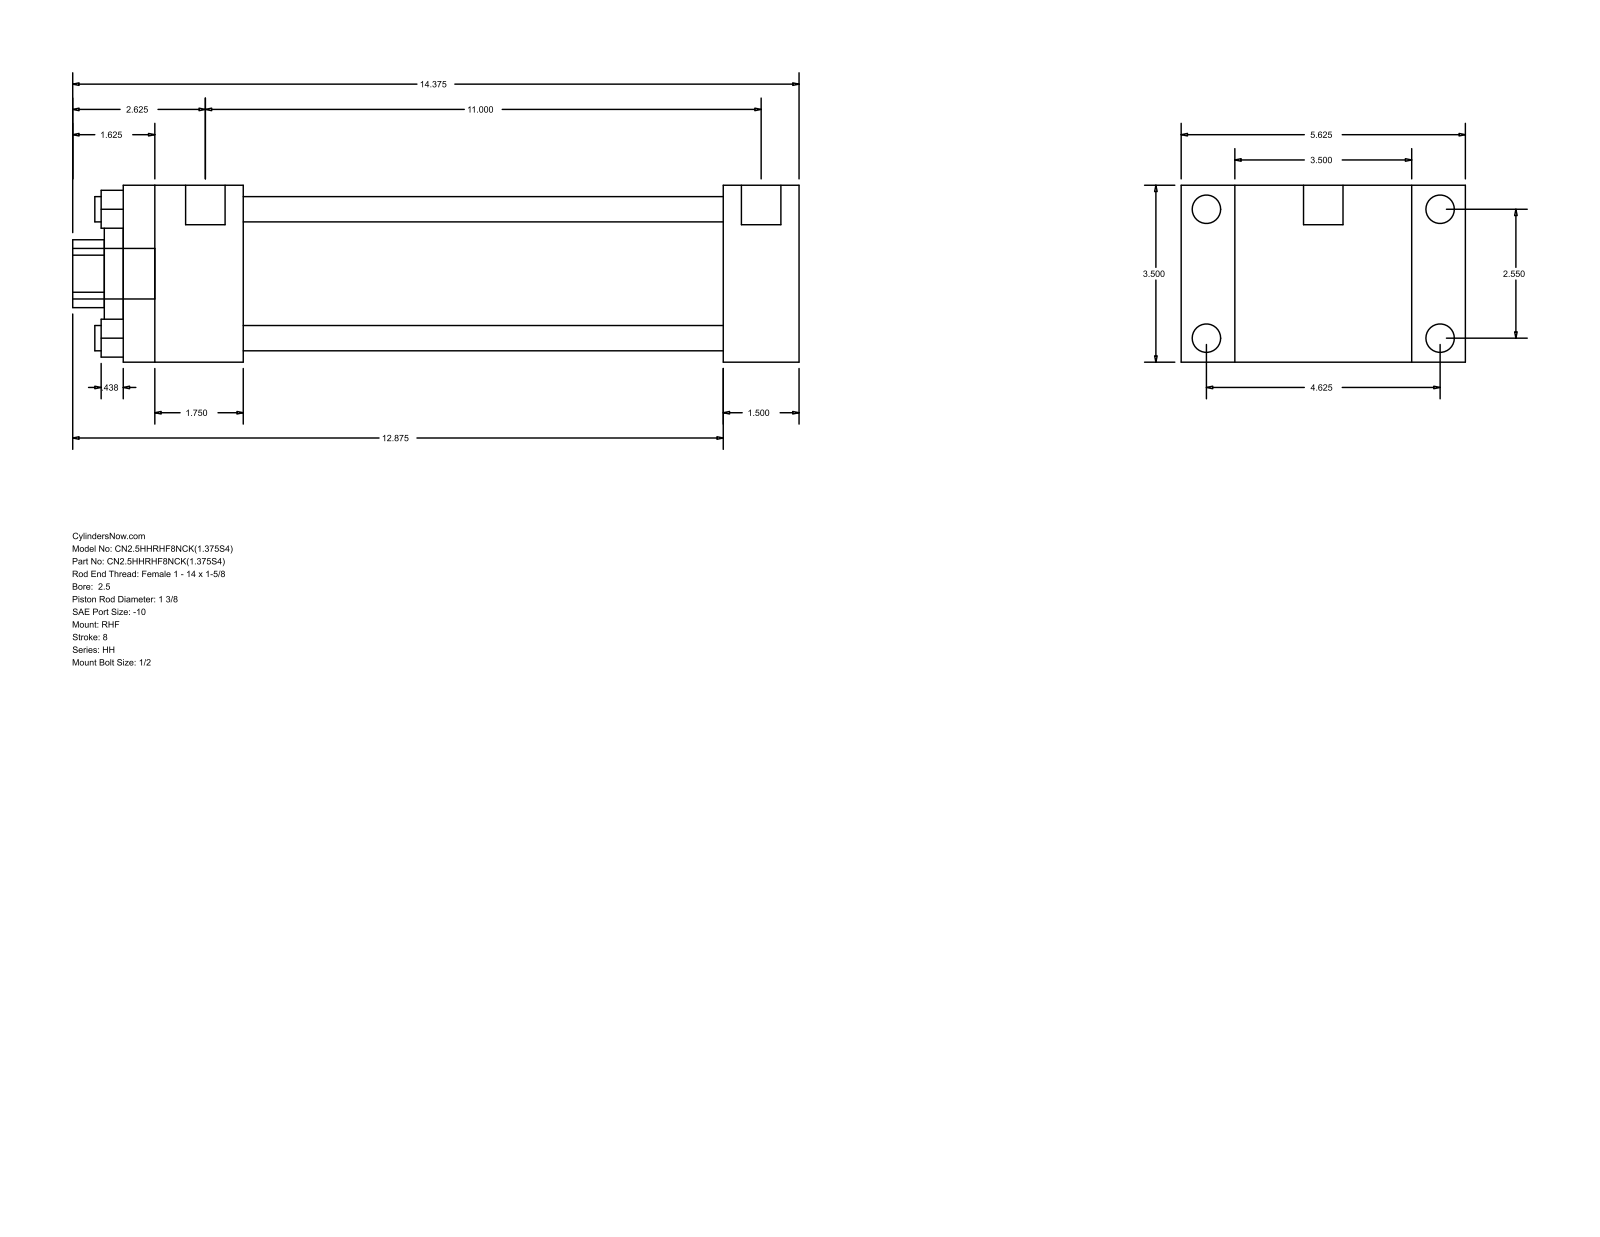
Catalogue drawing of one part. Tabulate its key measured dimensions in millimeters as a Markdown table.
| quantity | value |
| --- | --- |
| part name | HH_RHF__0250_1.375 |
| STEP written by | GSSL Pune (CONFIG_CONTROL_DESIGN) |
| units | millimeters |
| bodies | 0 solids, 88 faces (60 planar, 28 cylindrical, 0 other) |
| overall size | 365.12 × 142.88 × 88.9 |
| round holes (diameter × count) | 12.7 × 4, 34.92 × 1, 50.8 × 1, 73.03 × 1 |
| round bosses / shafts (diameter × count) | 14.3 × 4, 5.56 × 4, 19.84 × 2, 25.4 × 1 |
| partial cylindrical surfaces (radius × count) | 17.06 × 1 |
| main face-to-face distances | 88.9, 38.1, 26.99, 115.89, 301.62, 339.72, 142.88, 60.32, 241.3, 279.4 |
| hole center spacings | 45.79, 64.76, 91.58 |
